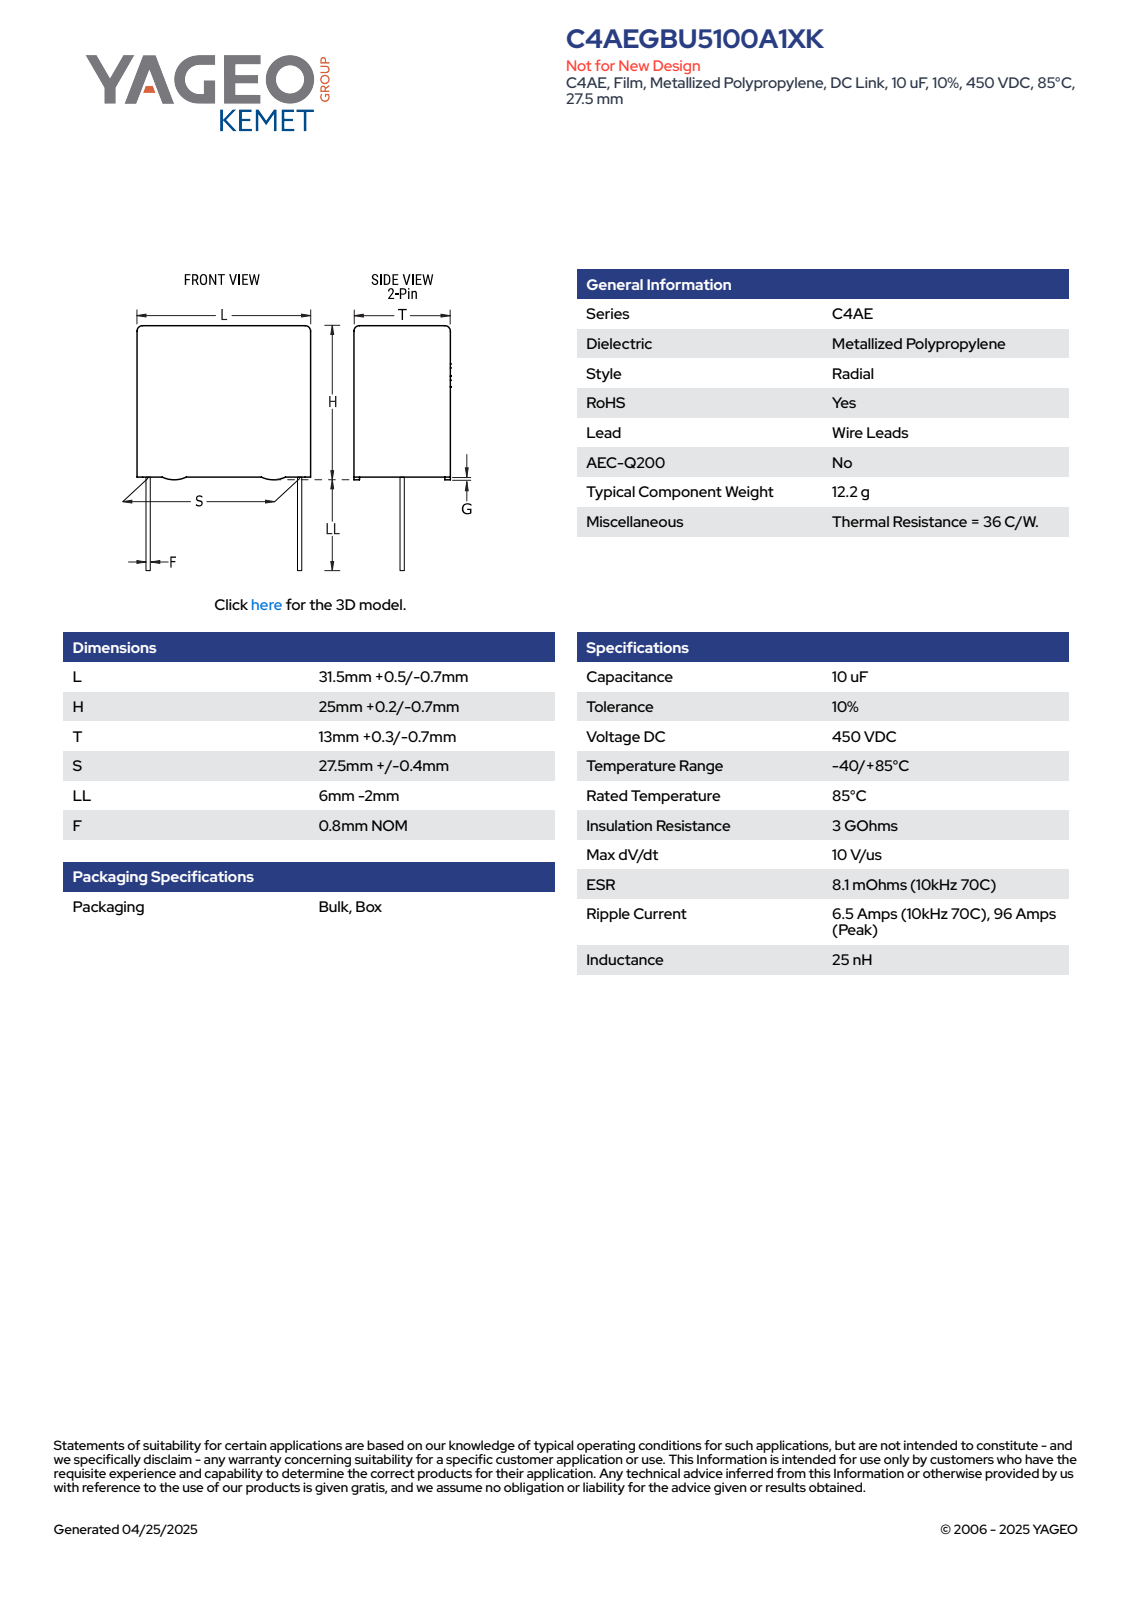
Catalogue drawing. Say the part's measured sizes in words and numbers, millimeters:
The part is named "CFP_RBG_31.5X25X13_L32H25.2T13.3S27.9LL4F0.8G0.5". Its 3-D file was written by "SolidWorks 2014 (AUTOMOTIVE_DESIGN)". It is 4 solids with 89 faces: 81 planar, 8 cylindrical and 0 other. Overall it measures 32 by 29.2 by 13.3 millimeters. Its volume is 10 524 cubic millimeters and its surface area 3 213 square millimeters. Round bosses or shafts: 2 of diameter 0.8. Partial cylindrical surfaces (rounded edges, fillets, slot ends): 4 of radius 0.5. The main face-to-face distances are 13.3, 24.7, 32, 0.5, 25.2, 1.18, 12.12, 10.94, 18.78, 4.
